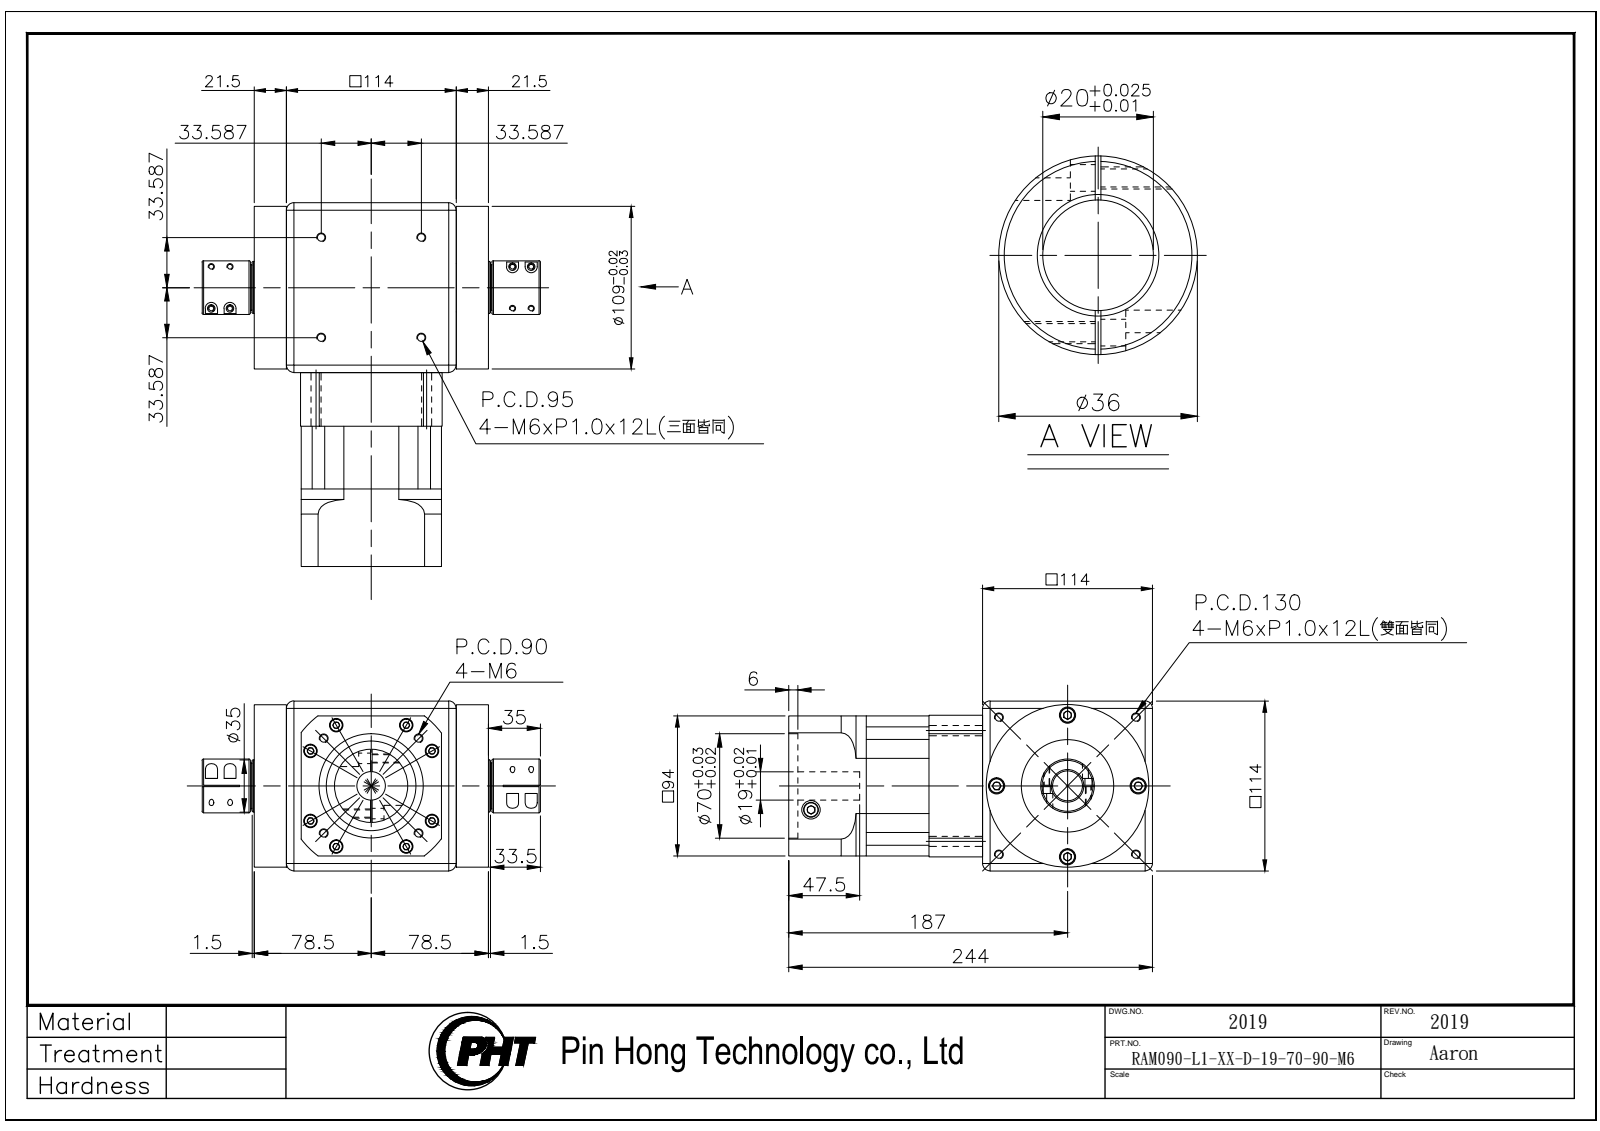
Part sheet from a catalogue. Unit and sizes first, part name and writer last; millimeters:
Units: millimetres
Overall size (bounding box): 244 × 227 × 114
Round holes (diameter × count): ⌀5 ×16, ⌀5.2 ×8, ⌀6 ×8, ⌀9 ×8, ⌀6.6 ×4, ⌀6.8 ×4, ⌀11 ×4, ⌀12.7 ×2, ⌀19 ×1, ⌀20 ×1, ⌀27 ×1, ⌀28 ×1
Round bosses / shafts (diameter × count): ⌀8.5 ×16, ⌀10 ×8, ⌀9.2 ×8, ⌀5 ×8, ⌀109 ×1, ⌀80 ×1, ⌀62 ×1, ⌀49 ×1
Partial cylindrical surfaces — rounded edges, fillets, slot ends (radius × count): R4.75 ×8, R2.55 ×4, R6 ×4, R50.5 ×1, R59 ×1, R79.1 ×1
Main face-to-face distances: 114, 10, 104, 78, 192, 94, 31.5, 104.5, 9.5, 0.5
Hole centre spacings: 47, 67.18, 12.17, 12.34, 14.08, 45.99, 47.5, 56.03
Volume: 2 791 000 mm³ · Surface area: 252 905 mm²
Bodies: 3 solids, 1007 faces (496 planar, 336 cylindrical, 175 other)
Part name (STEP PRODUCT): RAM090-L1-XX-D-19-70-90-M6_2019
STEP written by: SolidWorks 2016 (AUTOMOTIVE_DESIGN)
